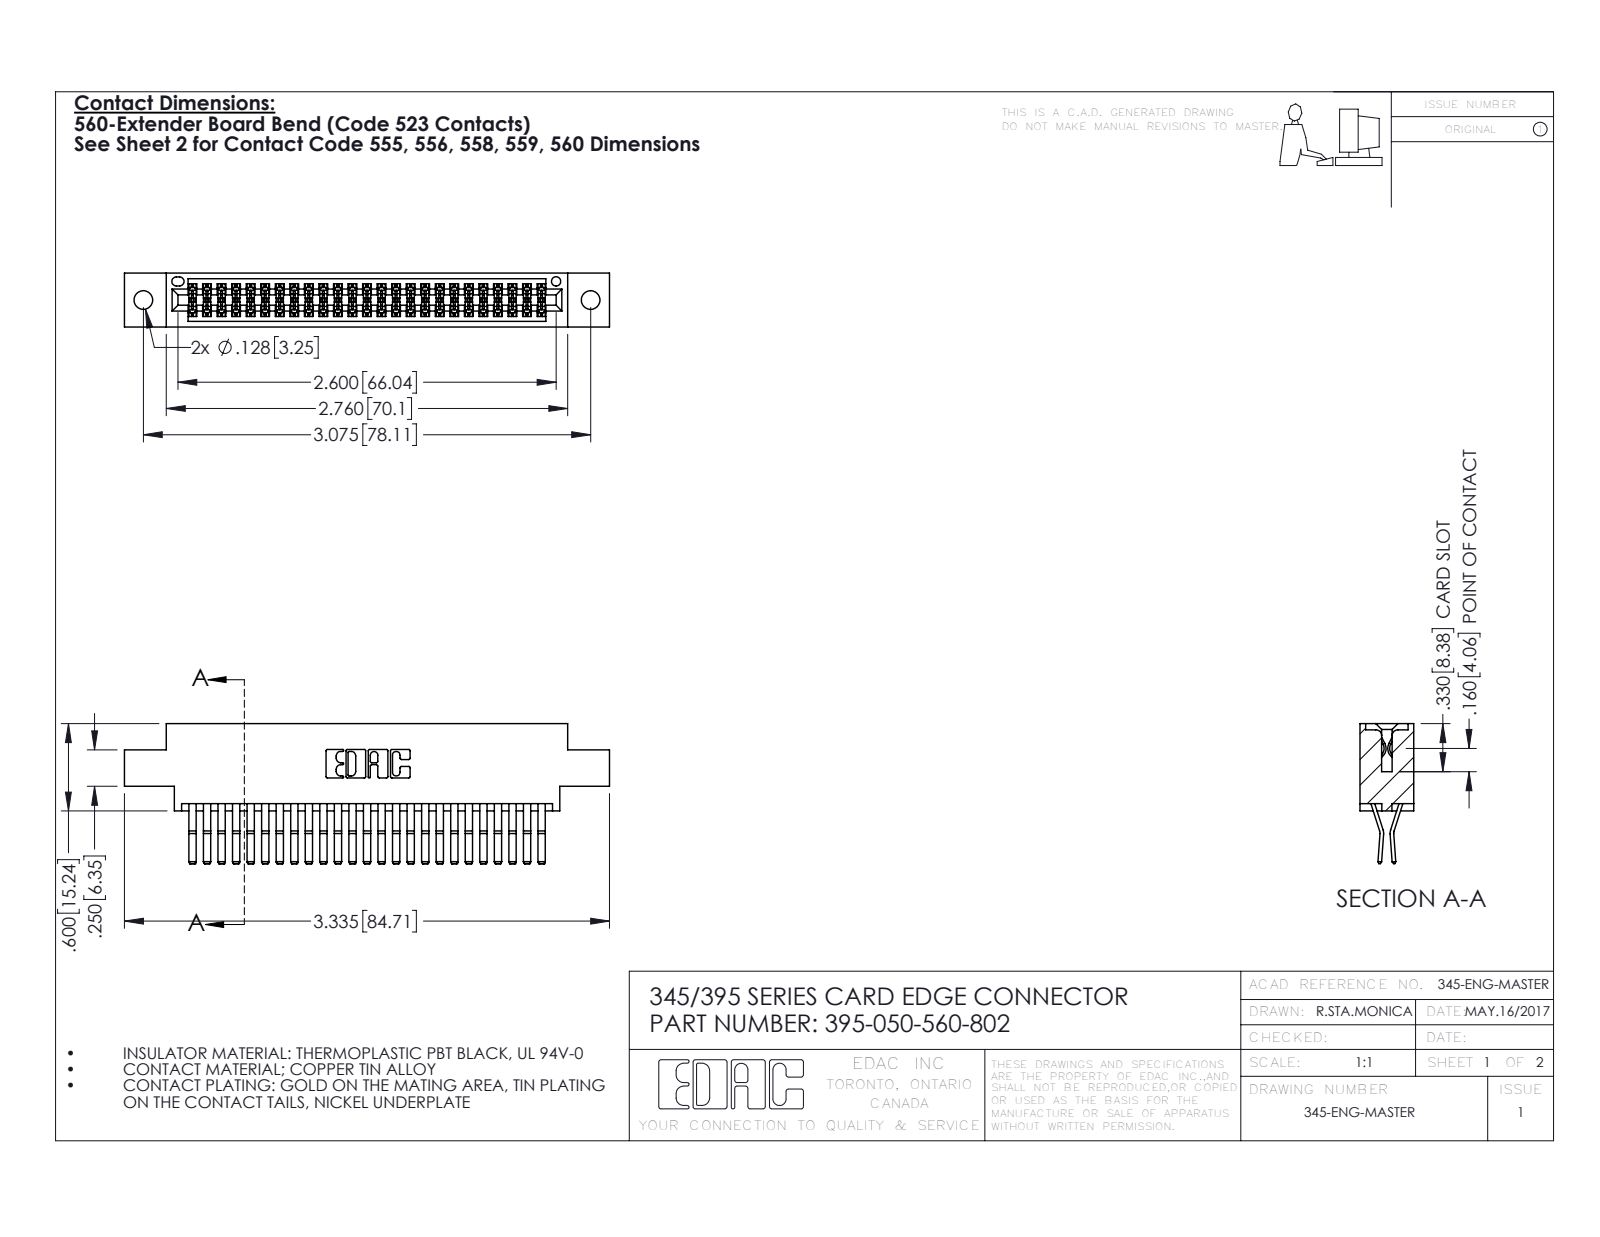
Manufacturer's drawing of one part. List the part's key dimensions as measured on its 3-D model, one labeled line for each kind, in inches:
Part name (STEP PRODUCT): 345-292-001_560 Tail; 345 Part_0.170 Offset - 0.128 Dia; 395-050-560-802
STEP written by: SolidWorks 2016 (CONFIG_CONTROL_DESIGN)
Units: inches
Bodies: 51 solids, 2730 faces (1734 planar, 996 cylindrical, 0 other)
Overall size (bounding box): 3.335 × 0.962 × 0.37
Volume: 0.503 in³ · Surface area: 19.49 in²
Round holes (diameter × count): ⌀0.128 ×2, ⌀0.064 ×1
Partial cylindrical surfaces — rounded edges, fillets, slot ends (radius × count): R0.006 ×76, R0.01 ×22, R0.007 ×6, R0.031 ×6, R0.026 ×3, R0.01 ×2, R0.014 ×2, R0.019 ×2
Main face-to-face distances: 0.025, 0.298, 0.072, 0.37, 0.2, 0.098, 0.272, 0.225, 0.175, 0.149
Hole centre spacings: 0.27, 2.84, 3.075
